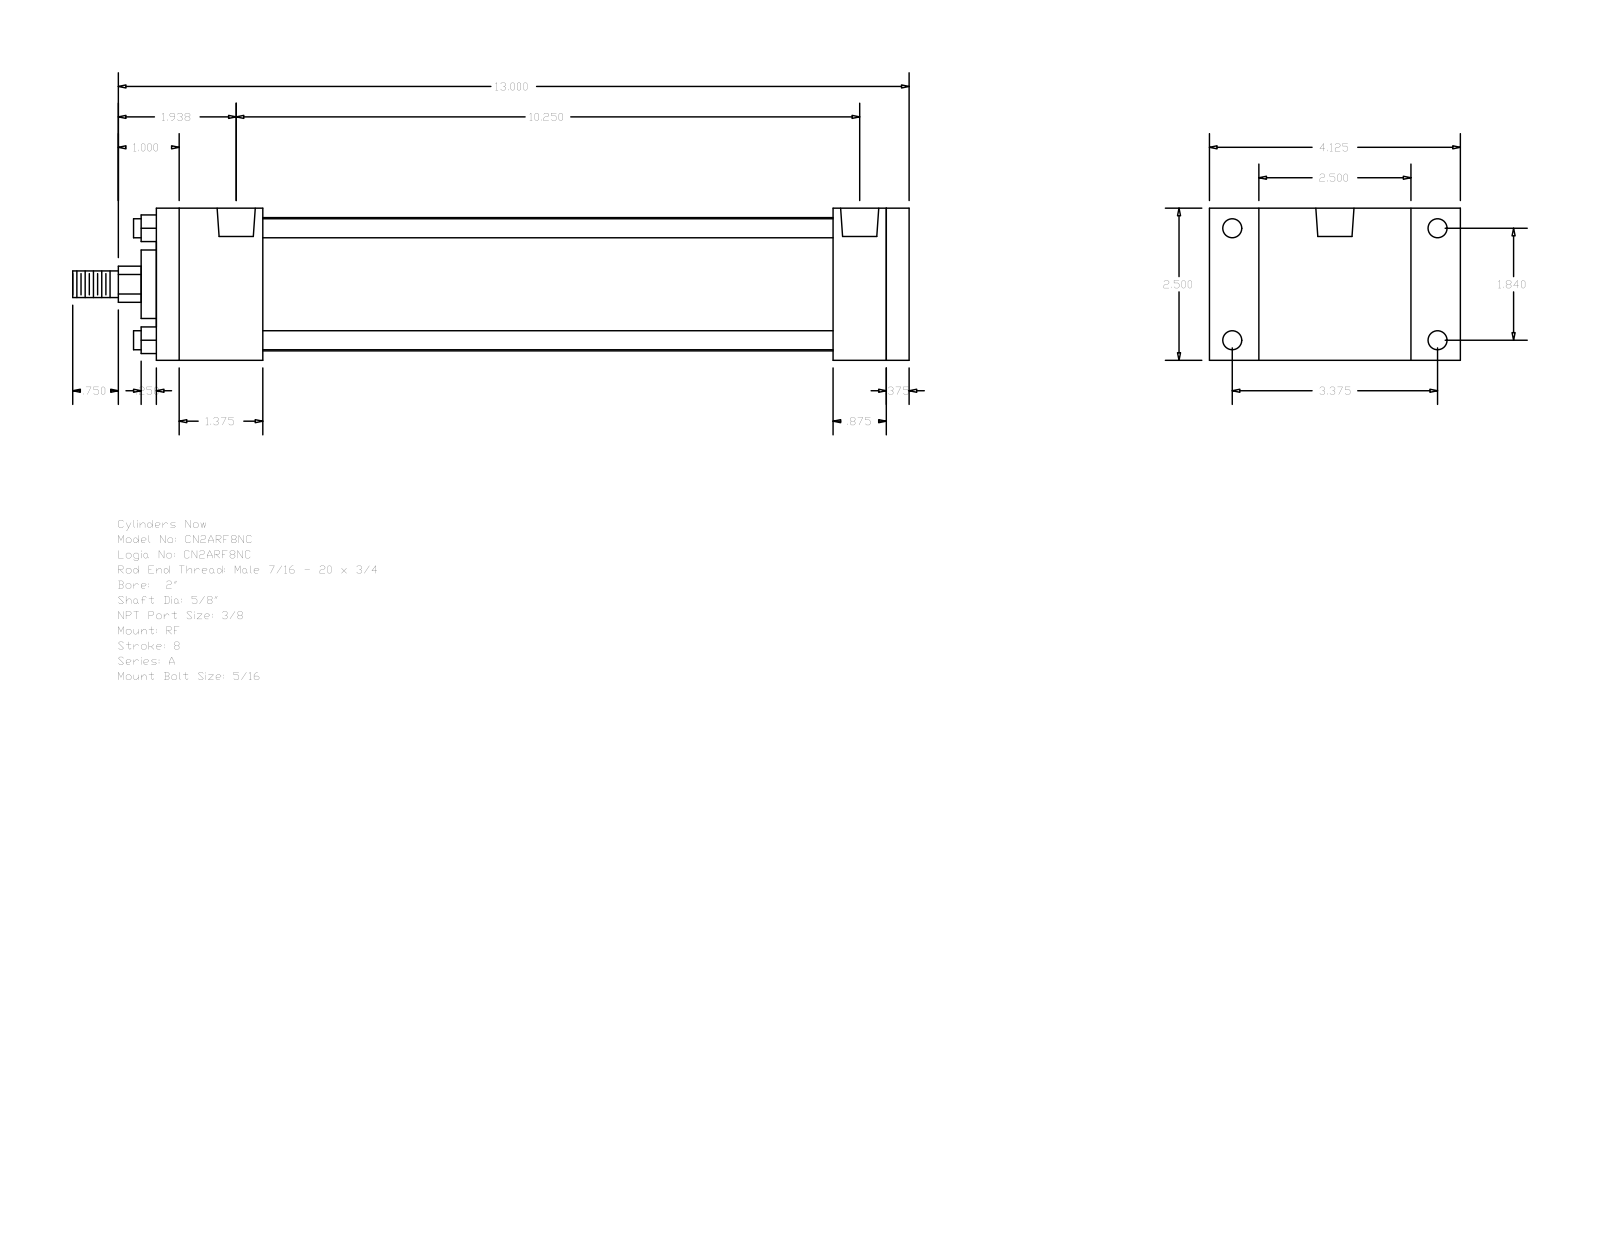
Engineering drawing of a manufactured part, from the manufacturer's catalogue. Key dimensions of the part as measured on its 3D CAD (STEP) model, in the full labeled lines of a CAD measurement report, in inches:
Part name (STEP PRODUCT): A_RF__0200_0.625
STEP written by: GSSL Pune (CONFIG_CONTROL_DESIGN)
Units: inches
Bodies: 0 solids, 92 faces (64 planar, 28 cylindrical, 0 other)
Overall size (bounding box): 13.75 × 4.125 × 2.5
Round holes (diameter × count): ⌀0.219 ×4, ⌀0.313 ×4, ⌀0.627 ×2
Round bosses / shafts (diameter × count): ⌀0.313 ×4, ⌀2.19 ×1, ⌀1.125 ×1, ⌀0.625 ×1, ⌀0.437 ×1
Partial cylindrical surfaces — rounded edges, fillets, slot ends (radius × count): R0.297 ×1
Main face-to-face distances: 2.5, 12.375, 12, 0.375, 1.75, 10.25, 10.625, 11.125, 9.375, 0.875
Hole centre spacings: 1.84, 3.375, 3.844, 9.937, 0.156, 0.157, 10.093, 10.094
